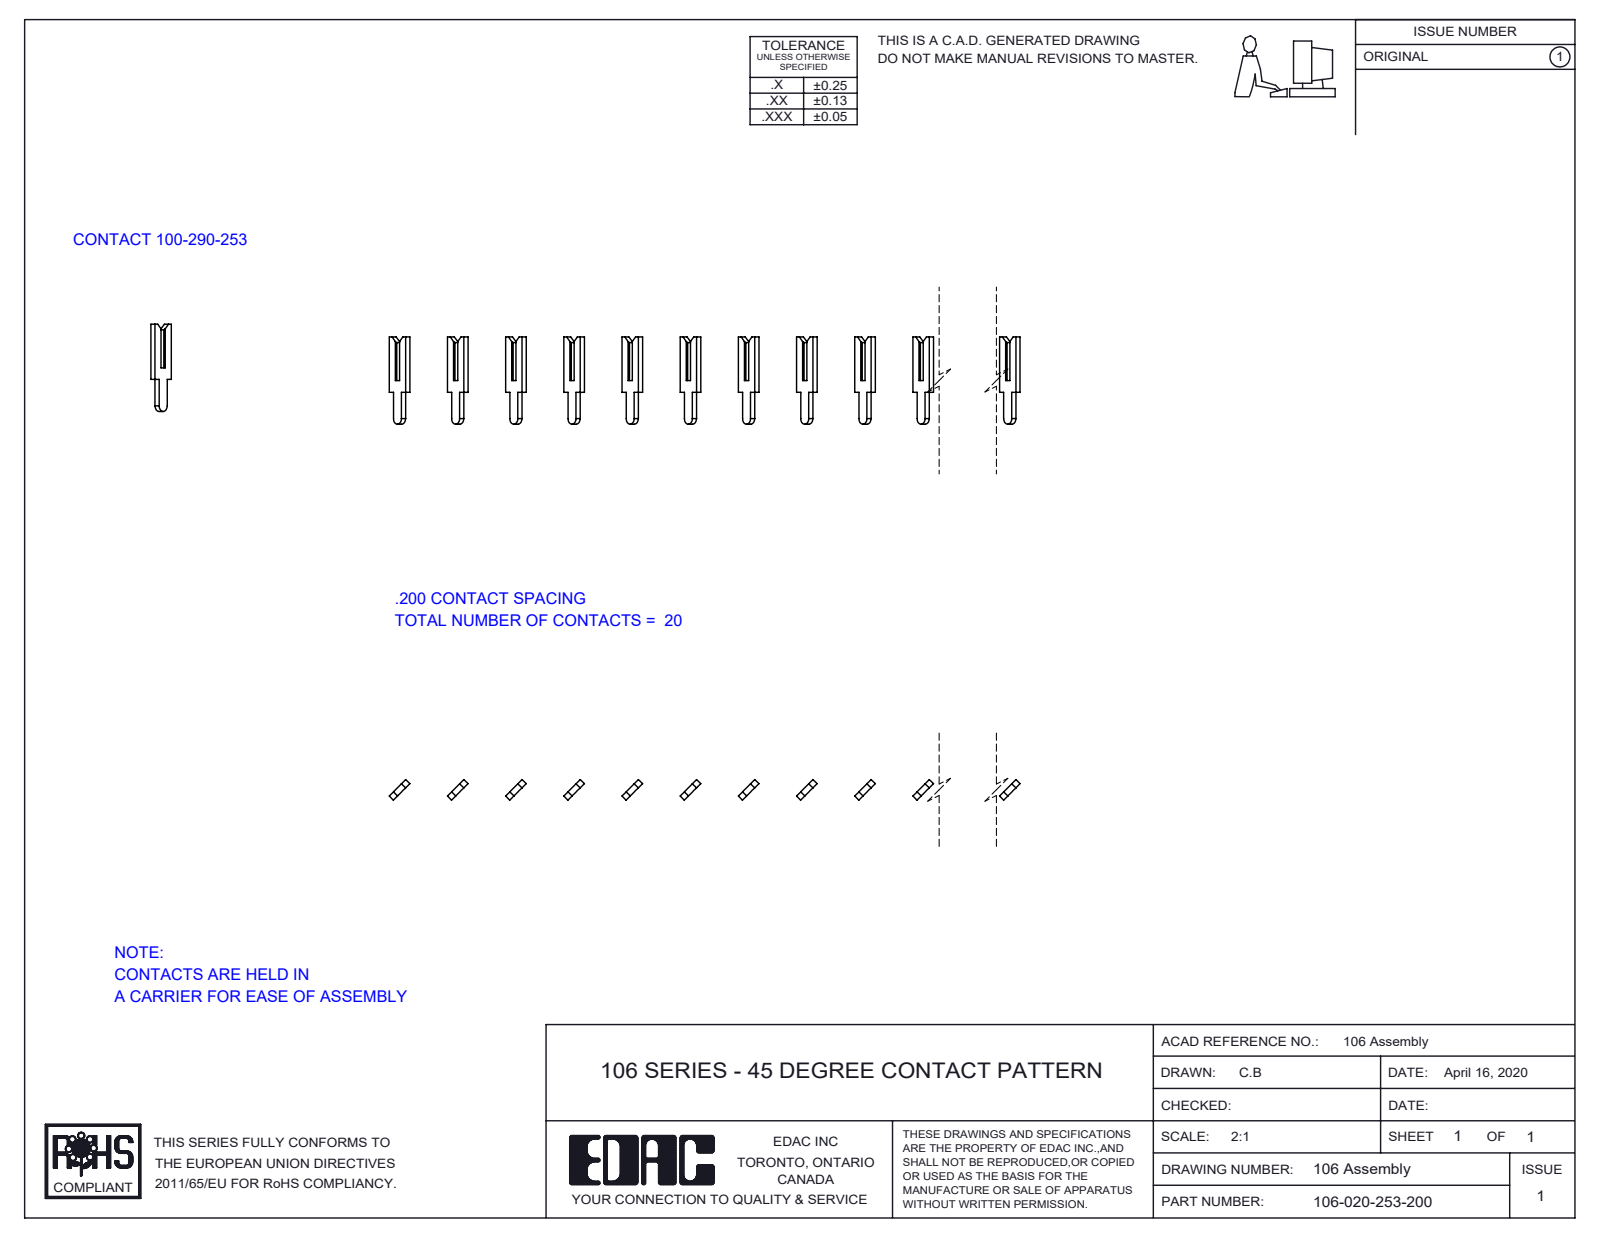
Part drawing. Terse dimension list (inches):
name: 106-020-253-200; 100-290-001_100-290-253
written by: SolidWorks 2016 (CONFIG_CONTROL_DESIGN)
unit: in
bodies: 20 solids, 400 faces (380 planar, 20 cylindrical, 0 other)
size: 3.871 × 0.3 × 0.071
volume: 0.007 in³; area: 1.067 in²
rounds: 20× R0.019
face distances: 0.141, 0.283, 0.566, 0.707, 0.848, 0.424, 0.424, 0.161, 0.283, 0.02
